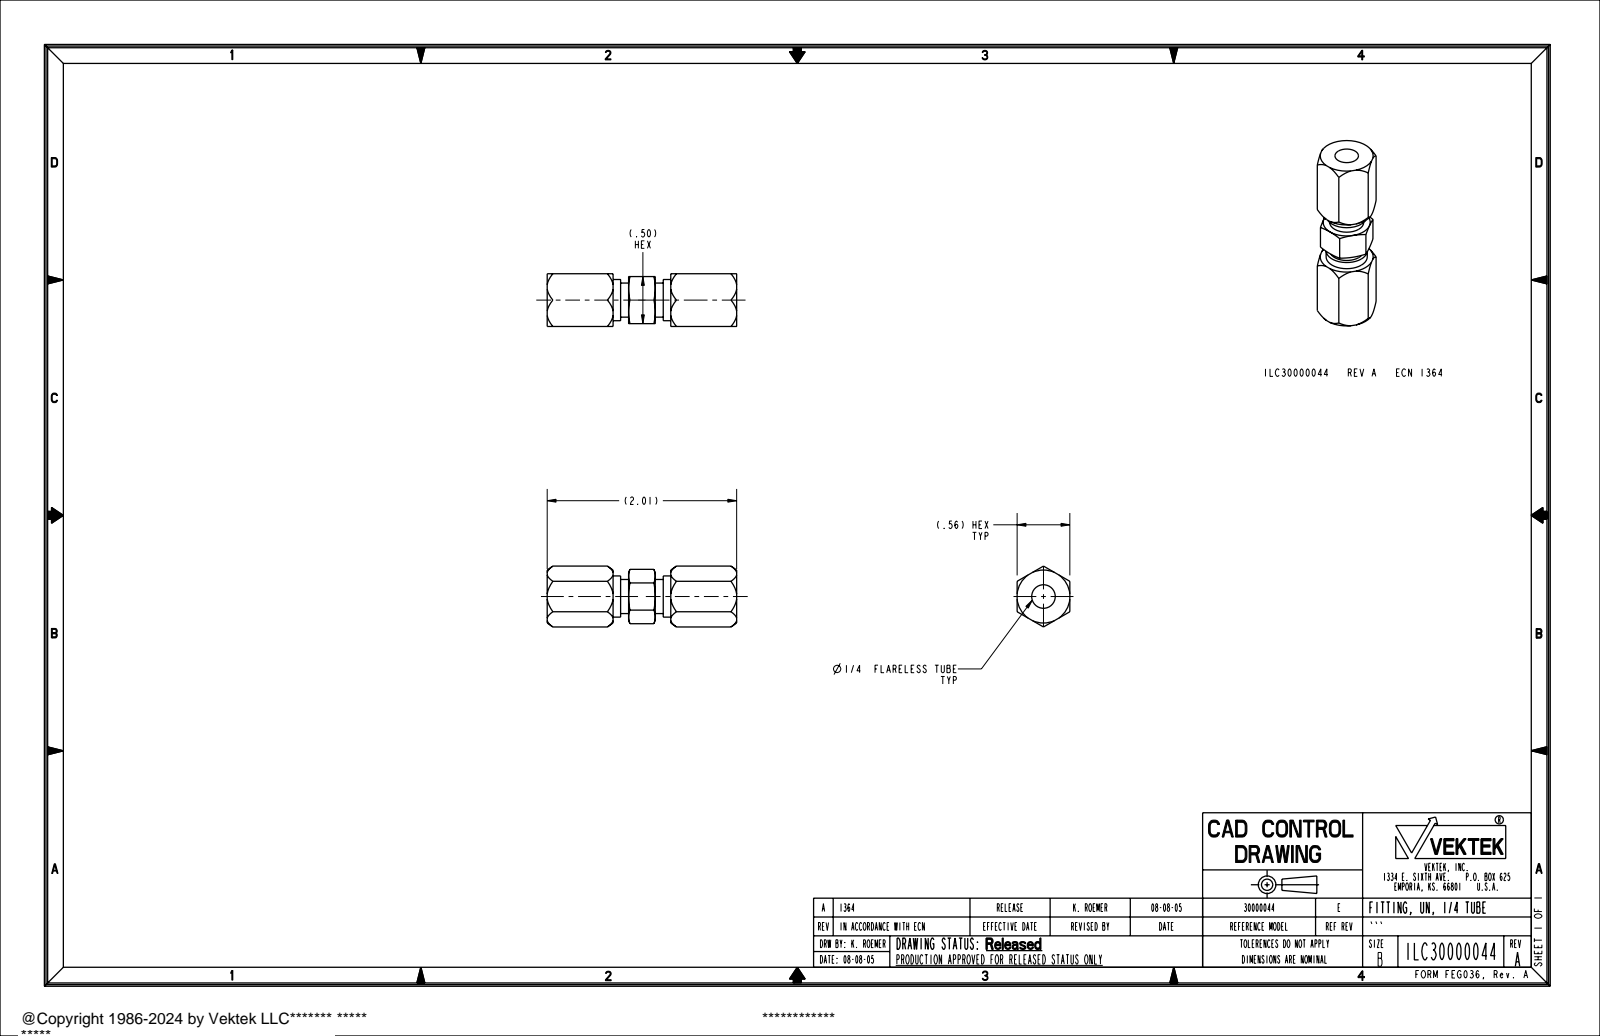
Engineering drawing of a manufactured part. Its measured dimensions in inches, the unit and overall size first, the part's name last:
Units: inches
Overall size (bounding box): 2.013 × 0.647 × 0.56
Round holes (diameter × count): ⌀0.25 ×1
Round bosses / shafts (diameter × count): ⌀0.437 ×1, ⌀0.362 ×1
Main face-to-face distances: 0.56, 0.03, 0.53, 0.5, 2.013, 0.7, 1.313, 0.865, 1.148, 0.165
Volume: 0.382 in³ · Surface area: 6.113 in²
Bodies: 1 solid, 72 faces (26 planar, 10 cylindrical, 36 other)
Part name (STEP PRODUCT): ILC30000044
STEP written by: PRO/ENGINEER BY PARAMETRIC TECHNOLOGY CORPORATION, 2004290 (AUTOMOTIVE_DESIGN_CC2)
